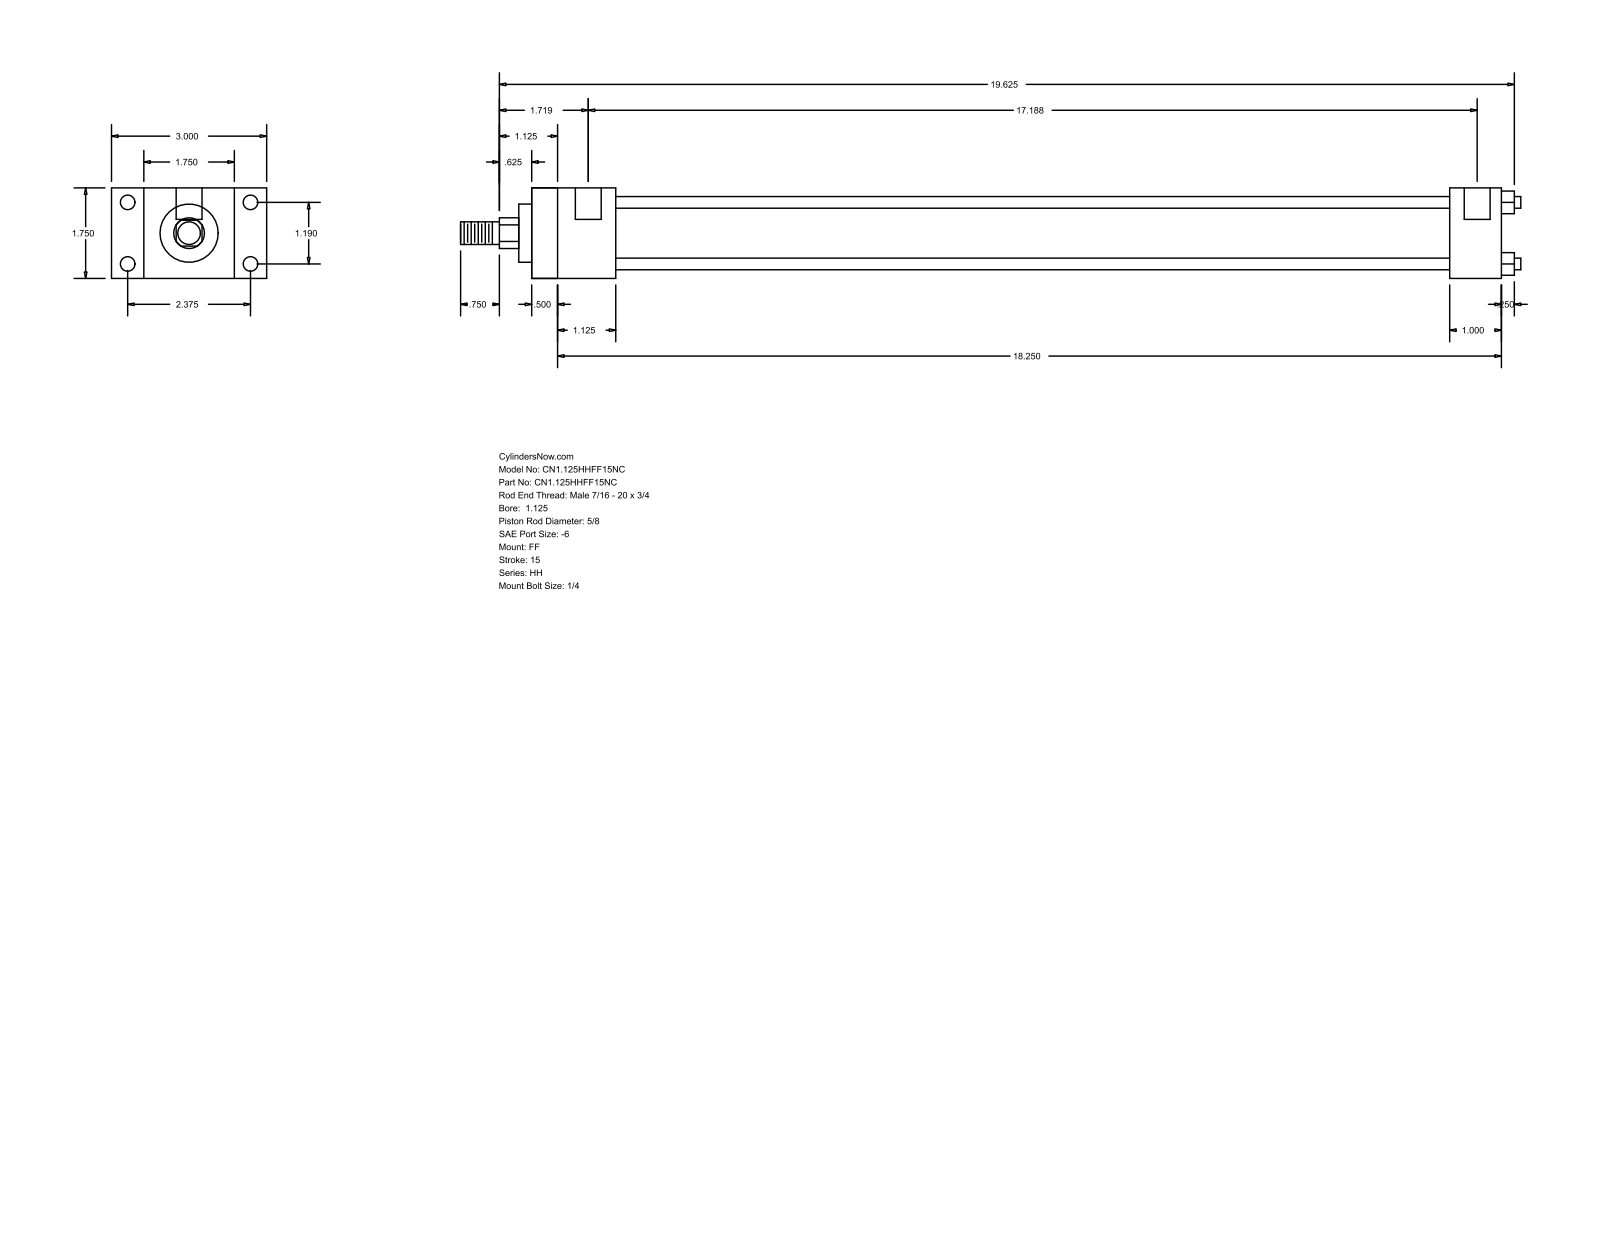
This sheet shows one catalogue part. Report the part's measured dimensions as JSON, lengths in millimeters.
{"part_name": "HH_FF__0112_0.625", "step_written_by": "GSSL Pune (CONFIG_CONTROL_DESIGN)", "units": "millimeters", "bodies": {"solids": 0, "faces": 92, "planar": 64, "cylindrical": 28, "other": 0}, "overall_size": [520.7, 76.2, 44.45], "round_holes": [[5.56, 4], [7.14, 4], [12.7, 2]], "round_bosses_or_shafts": [[5.71, 4], [34.92, 1], [28.57, 1], [15.88, 1], [11.11, 1]], "partial_cylinders_radius": [[7.54, 1]], "face_to_face_distances": [44.46, 476.24, 15.87, 12.69, 463.55, 28.58, 60.33, 41.27, 450.85, 438.16], "hole_center_spacings": [30.22, 60.32, 67.47, 433.39, 3.17, 436.56]}
